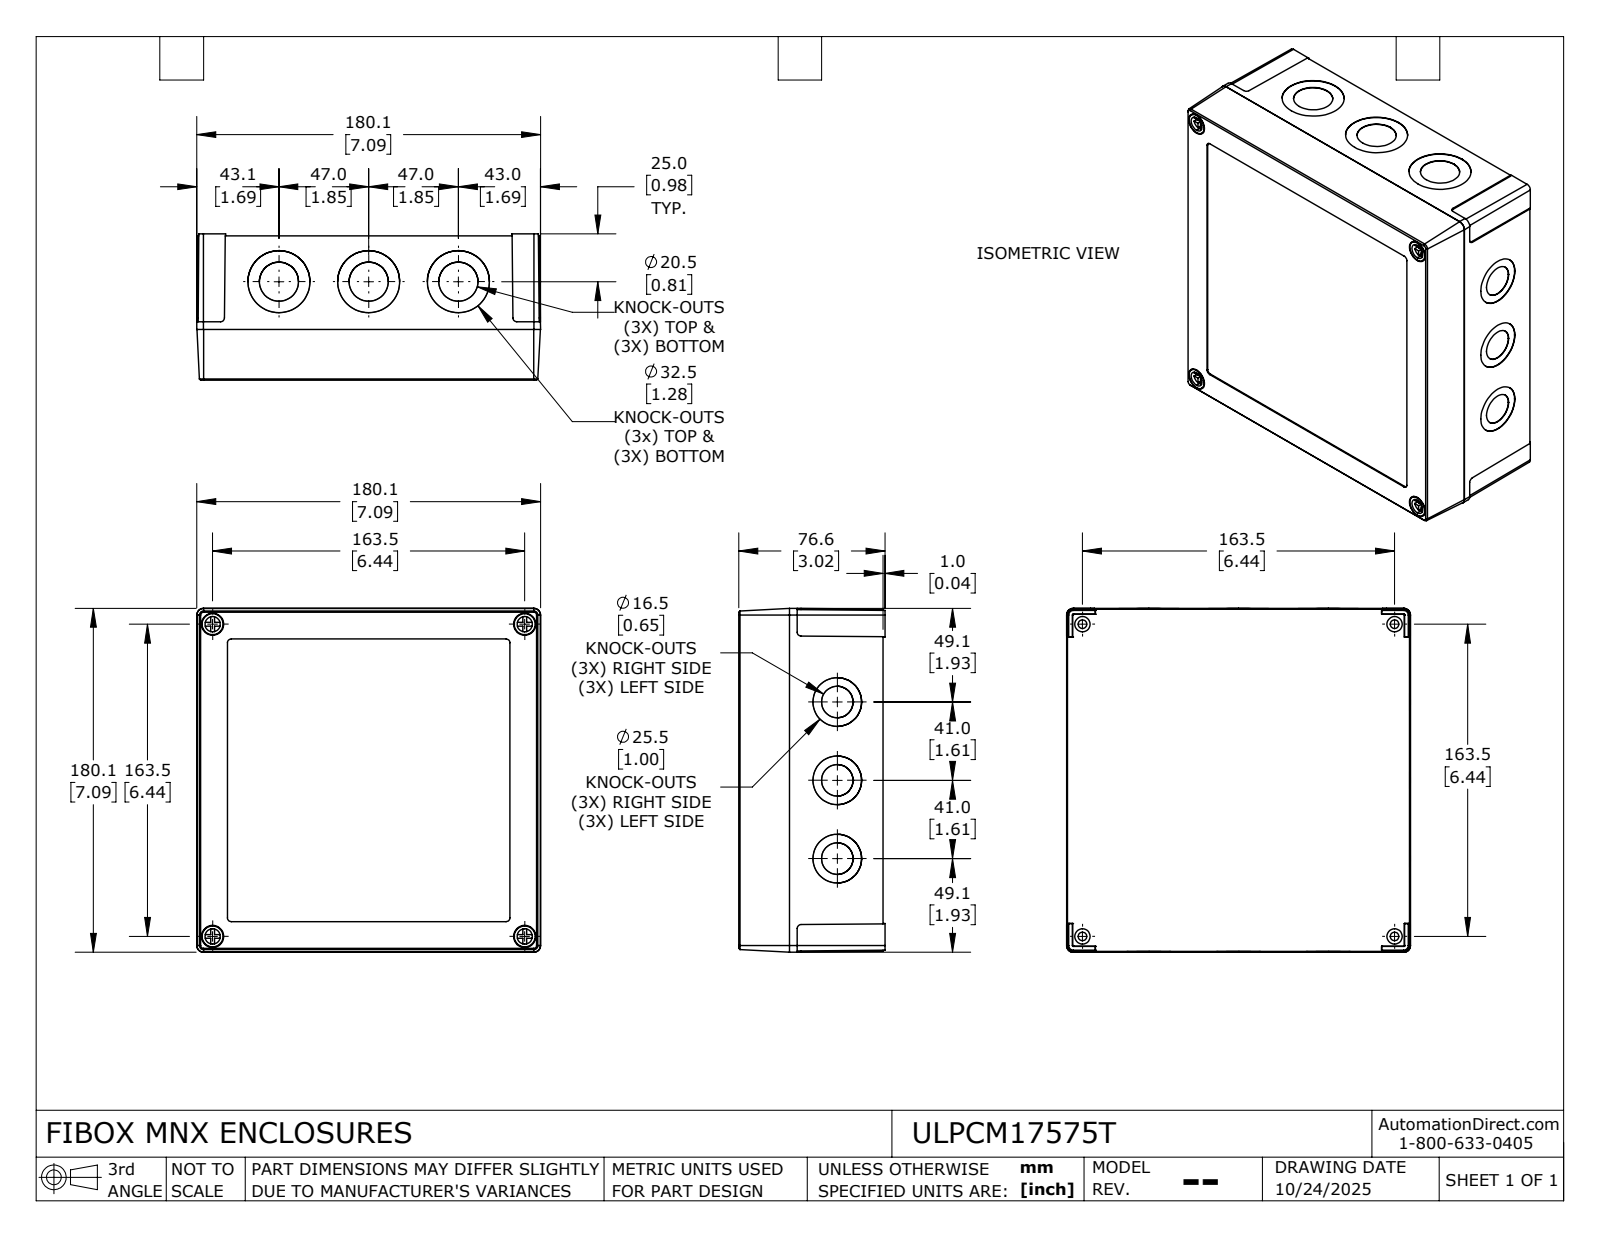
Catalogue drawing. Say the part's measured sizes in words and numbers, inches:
The part is named "ULPCM17575T_Default". Its 3-D file was written by "SolidWorks 2024 (CONFIG_CONTROL_DESIGN)". It is 6 solids with 582 faces: 318 planar, 224 cylindrical and 40 other. Overall it measures 7.091 by 7.091 by 3.016 inches. Its volume is 24.13 cubic inches and its surface area 381.4 square inches. Round holes: 12 of diameter 0.126, 12 of diameter 0.157, 6 of diameter 0.65, 6 of diameter 0.807, 6 of diameter 1.004, 6 of diameter 1.28, 4 of diameter 0.177, 4 of diameter 0.315, 4 of diameter 0.457. Round bosses or shafts: 12 of diameter 0.315, 8 of diameter 0.098, 4 of diameter 0.433, 4 of diameter 0.283. Partial cylindrical surfaces (rounded edges, fillets, slot ends): 8 of radius 0.079, 6 of radius 0.112, 4 of radius 0.042, 4 of radius 0.197, 2 of radius 0.046. The main face-to-face distances are 2.858, 0.118, 2.74, 0.165, 0.098, 2.957, 2.839, 2.976, 0.02, 1.811. The hole center spacings are 1.333, 1.969, 2.866, 3.252, 4.79, 5.207, 5.469, 5.853.
